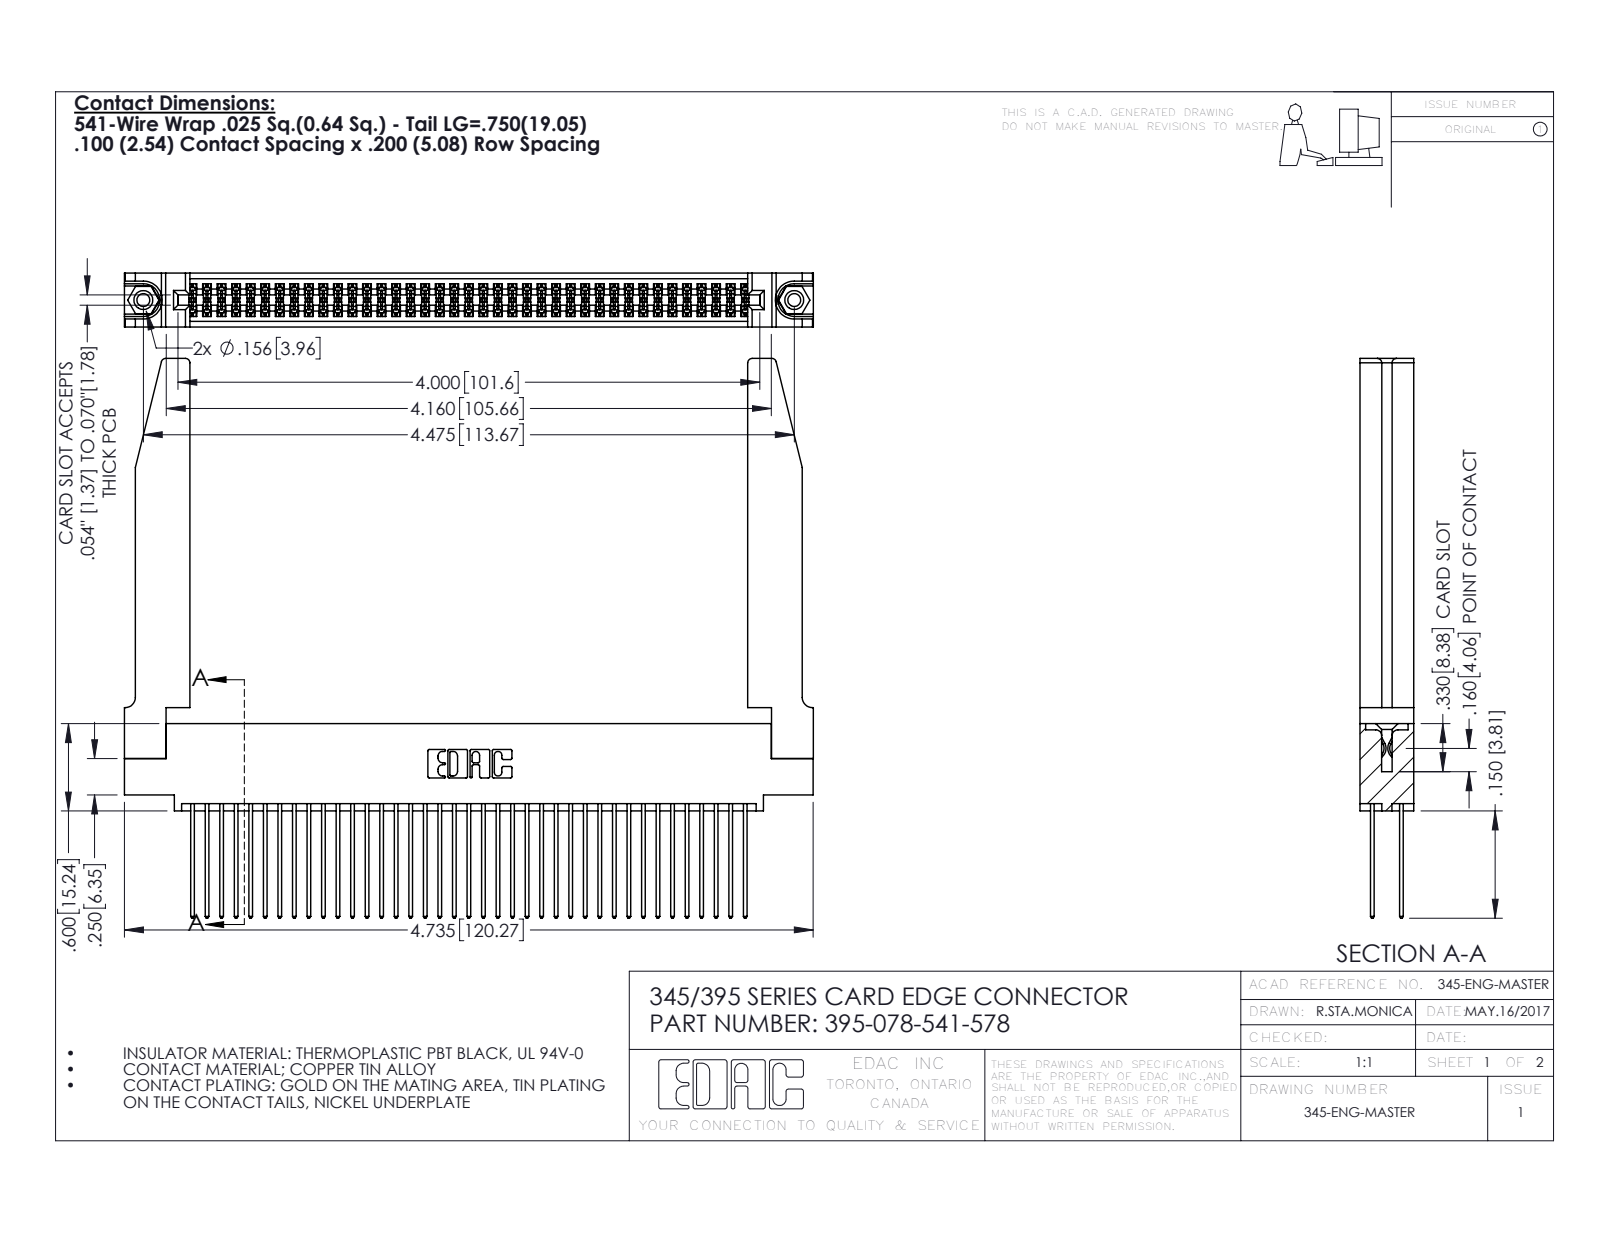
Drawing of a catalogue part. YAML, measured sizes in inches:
part_name: "395-078-541-578; 345 Part_0.110 Offset - 0.156 Dia-TH; 345-220-078_345-220-078; 345-292-001_345-293-141 (+1 more)"
step_written_by: "SolidWorks 2016 (CONFIG_CONTROL_DESIGN)"
units: inches
bodies: {solids: 83, faces: 4264, planar: 2800, cylindrical: 1412, other: 52}
overall_size: [4.736, 3.847, 0.37]
volume: 1.208
surface_area: 41.48
round_holes:
  - {diameter: 0.089, count: 2}
  - {diameter: 0.125, count: 2}
  - {diameter: 0.156, count: 2}
  - {diameter: 0.064, count: 1}
round_bosses_or_shafts:
  - {diameter: 0.155, count: 2}
partial_cylinders:
  - {radius: 0.006, count: 117}
  - {radius: 0.01, count: 78}
  - {radius: 0.01, count: 22}
  - {radius: 0.03, count: 8}
  - {radius: 0.007, count: 6}
  - {radius: 0.031, count: 6}
  - {radius: 0.026, count: 3}
  - {radius: 0.014, count: 2}
face_to_face_distances: [0.072, 0.298, 0.37, 0.2, 0.098, 0.272, 0.025, 0.225, 0.175, 0.148]
hole_center_spacings: [0.27, 4.239, 4.475]
